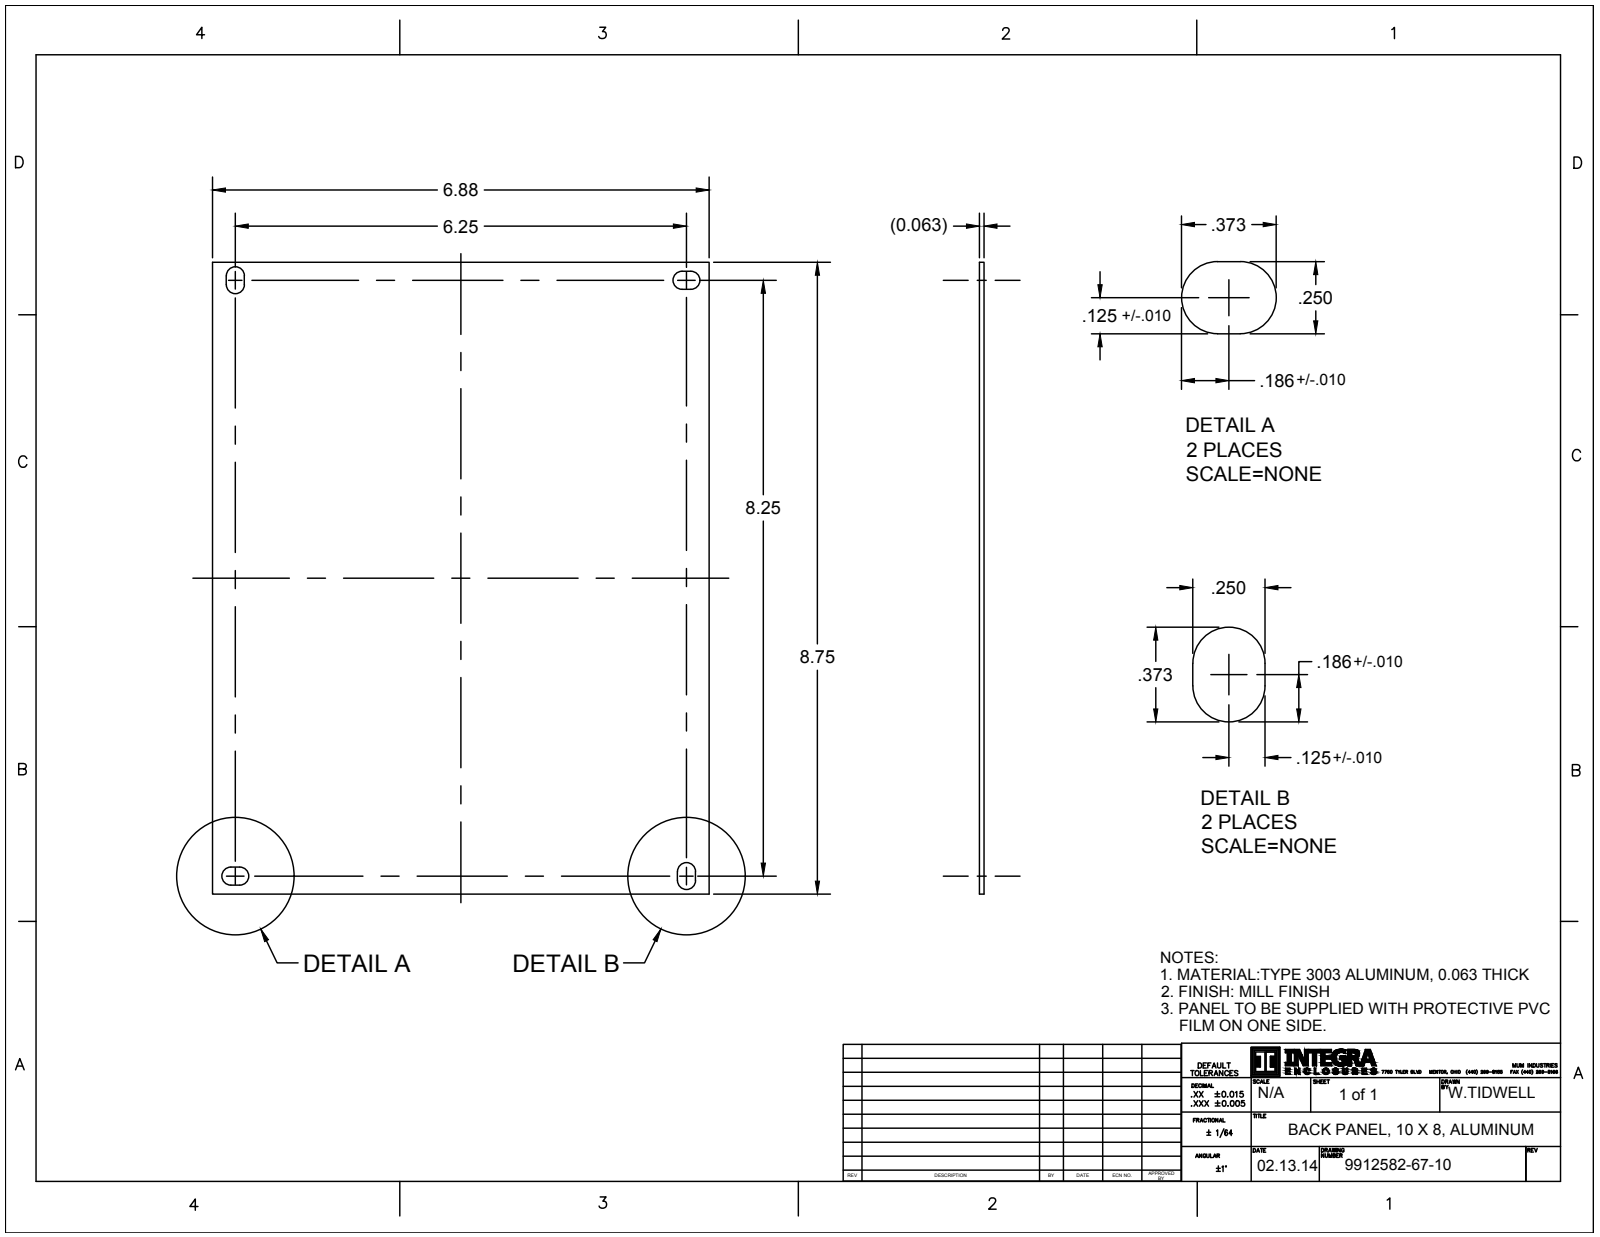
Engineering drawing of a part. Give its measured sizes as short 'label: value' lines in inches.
name: 9912582-67-10; 9912594-82-10; ABP108-IMP_ASM
written by: CREO PARAMETRIC BY PTC INC, 2016050 (CONFIG_CONTROL_DESIGN)
unit: in
bodies: 5 solids, 382 faces (122 planar, 152 cylindrical, 108 other)
size: 8.75 × 6.88 × 0.508
volume: 3.85 in³; area: 124.7 in²
bosses: 4× ⌀0.373, 4× ⌀0.19, 4× ⌀0.136
rounds: 8× R0.125
face distances: 0.063, 6.88, 8.75, 0.196, 0.133, 0.375, 0.12, 0.057, 0.076, 0.312
